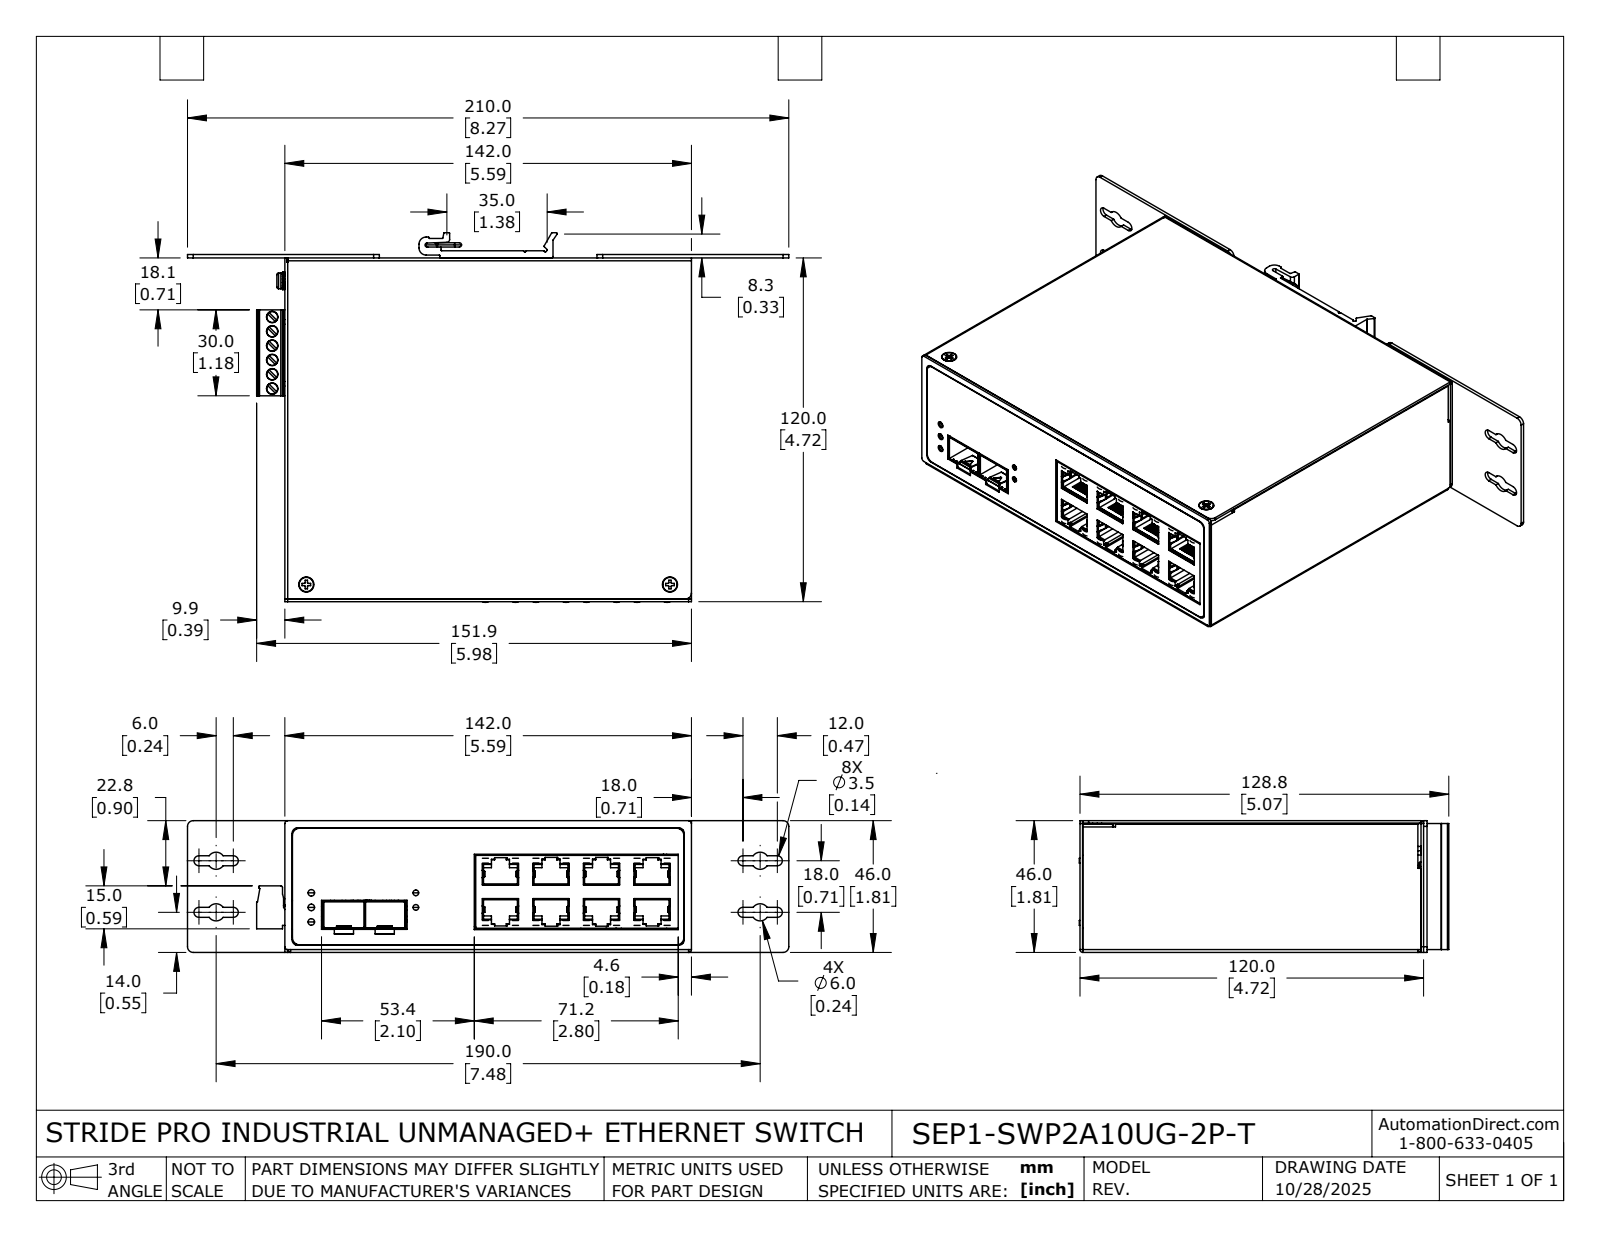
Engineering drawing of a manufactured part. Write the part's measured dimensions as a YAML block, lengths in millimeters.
part_name: "SEP1-SWP2A10UG-2P-T"
step_written_by: "SolidWorks 2024 (AUTOMOTIVE_DESIGN)"
units: millimeters
bodies: {solids: 83, faces: 5655, planar: 3980, cylindrical: 1358, other: 317}
overall_size: [151.8, 129.1, 46]
volume: 162700
surface_area: 221200
round_holes:
  - {diameter: 4, count: 18}
  - {diameter: 5.3, count: 7}
  - {diameter: 1.4, count: 6}
  - {diameter: 2, count: 5}
  - {diameter: 2.8, count: 5}
  - {diameter: 2.5, count: 4}
  - {diameter: 3.2, count: 4}
  - {diameter: 2.3, count: 3}
  - {diameter: 1, count: 2}
  - {diameter: 2.4, count: 2}
  - {diameter: 2.4, count: 2}
  - {diameter: 1.5, count: 1}
round_bosses_or_shafts:
  - {diameter: 3, count: 16}
  - {diameter: 0.5, count: 12}
  - {diameter: 5, count: 10}
  - {diameter: 3.8, count: 6}
  - {diameter: 1.5, count: 6}
  - {diameter: 4.2, count: 4}
  - {diameter: 4, count: 4}
  - {diameter: 3.8, count: 4}
partial_cylinders:
  - {radius: 0.1, count: 151}
  - {radius: 0.2, count: 137}
  - {radius: 0.3, count: 95}
  - {radius: 0.5, count: 48}
  - {radius: 0.2, count: 39}
  - {radius: 0.1, count: 32}
  - {radius: 1, count: 28}
  - {radius: 0.1, count: 22}
face_to_face_distances: [0.9, 45.1, 1.6, 31.6, 44.2, 7.2, 37, 37.9, 5.6, 38.6]
hole_center_spacings: [5, 10, 15, 20, 5.1, 36.9, 0.9, 10.6]
